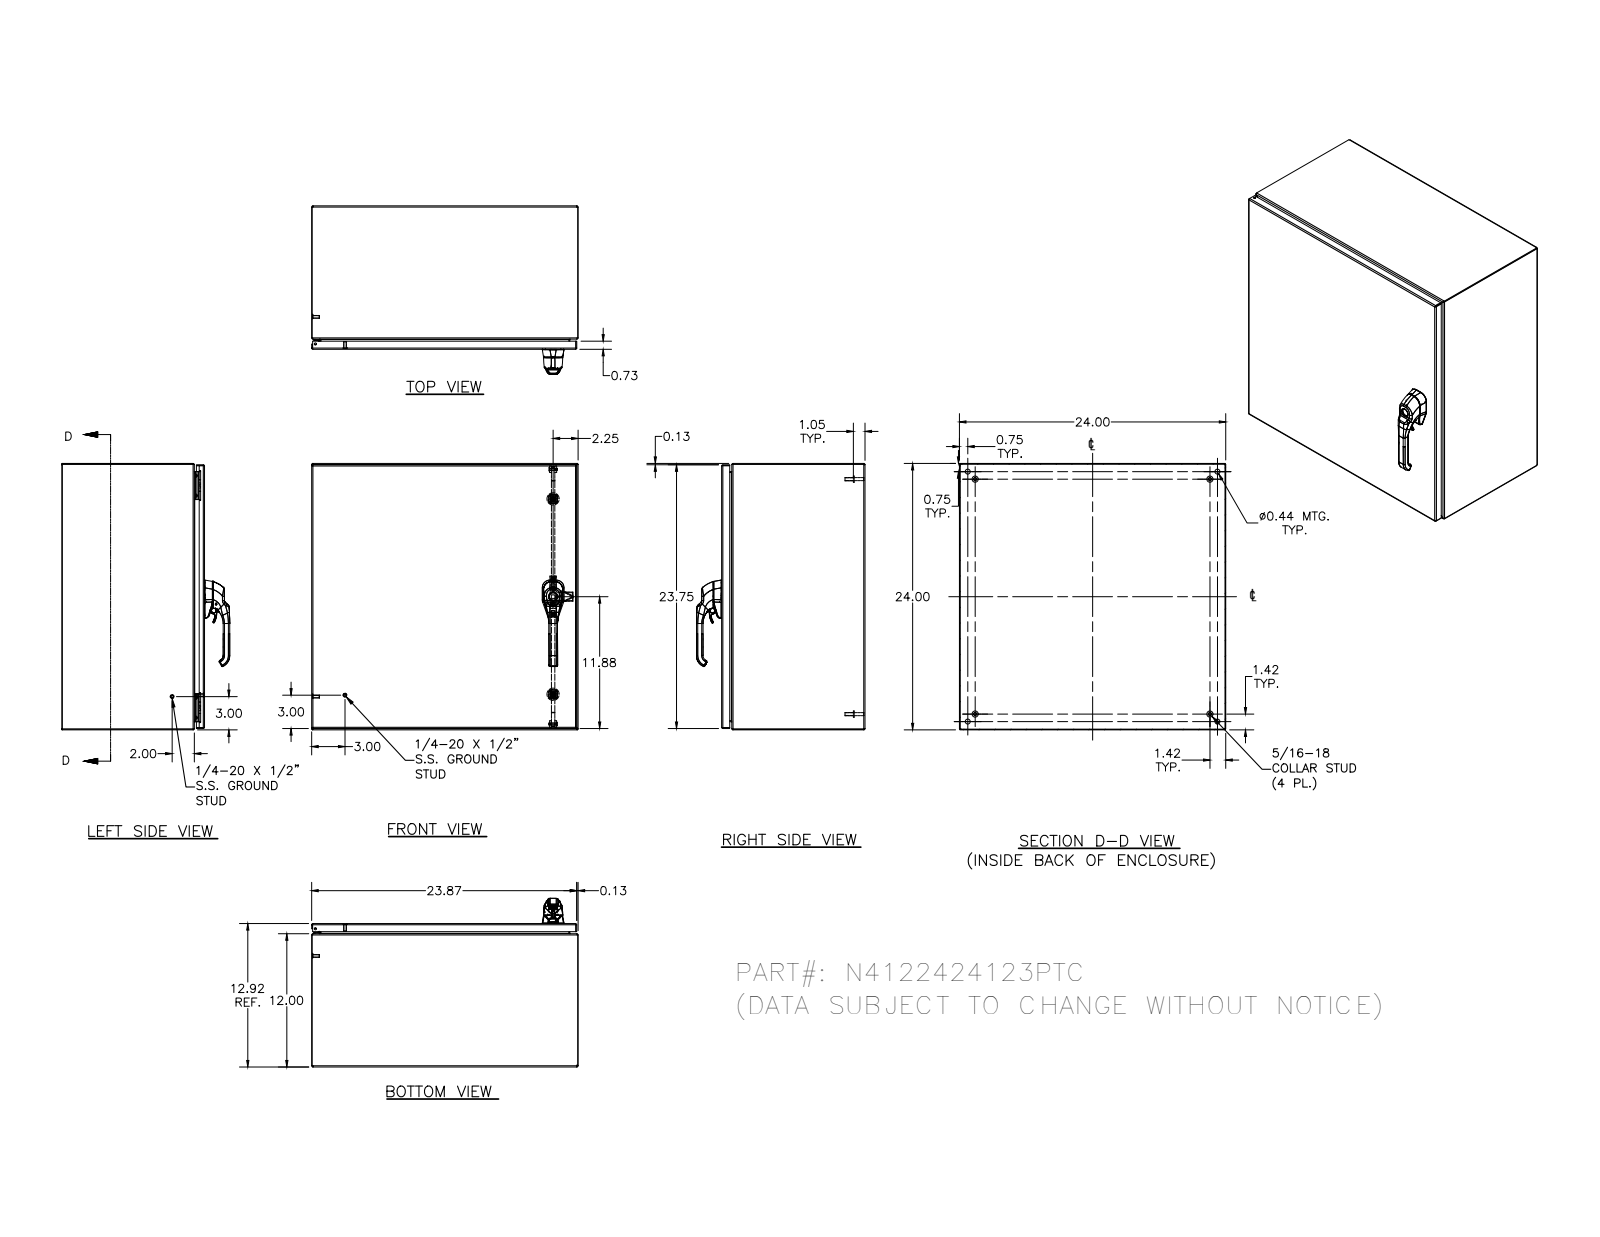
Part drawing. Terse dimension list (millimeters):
name: N4122424123PTC
written by: SolidWorks 2018 (AUTOMOTIVE_DESIGN)
unit: mm
bodies: 51 solids, 1644 faces (589 planar, 592 cylindrical, 463 other)
size: 609.6 × 609.6 × 383.4
volume: 3 241 000 mm³; area: 3 290 000 mm²
holes: 5× ⌀4.8, 4× ⌀2.4, 4× ⌀3.9, 4× ⌀4.2, 4× ⌀4.2, 4× ⌀4.4, 4× ⌀5, 4× ⌀11.1, 2× ⌀2.7, 2× ⌀4, 2× ⌀4.1, 2× ⌀4.3
bosses: 10× ⌀6.4, 4× ⌀14.3, 4× ⌀9.1, 4× ⌀8.1, 4× ⌀7.6, 4× ⌀7, 4× ⌀6.5, 4× ⌀6
rounds: 30× R0.8, 26× R1.3, 20× R2.7, 18× R0.4, 18× R0.5, 16× R3, 14× R3.2, 8× R0.8
face distances: 1.9, 607.7, 326.2, 605.8, 609.6, 328.1, 324.3, 302.9, 23.3, 18.8
hole spacings: 507.9, 571.5, 580.9, 0.4, 16.8, 524.7, 0.5, 12.7
